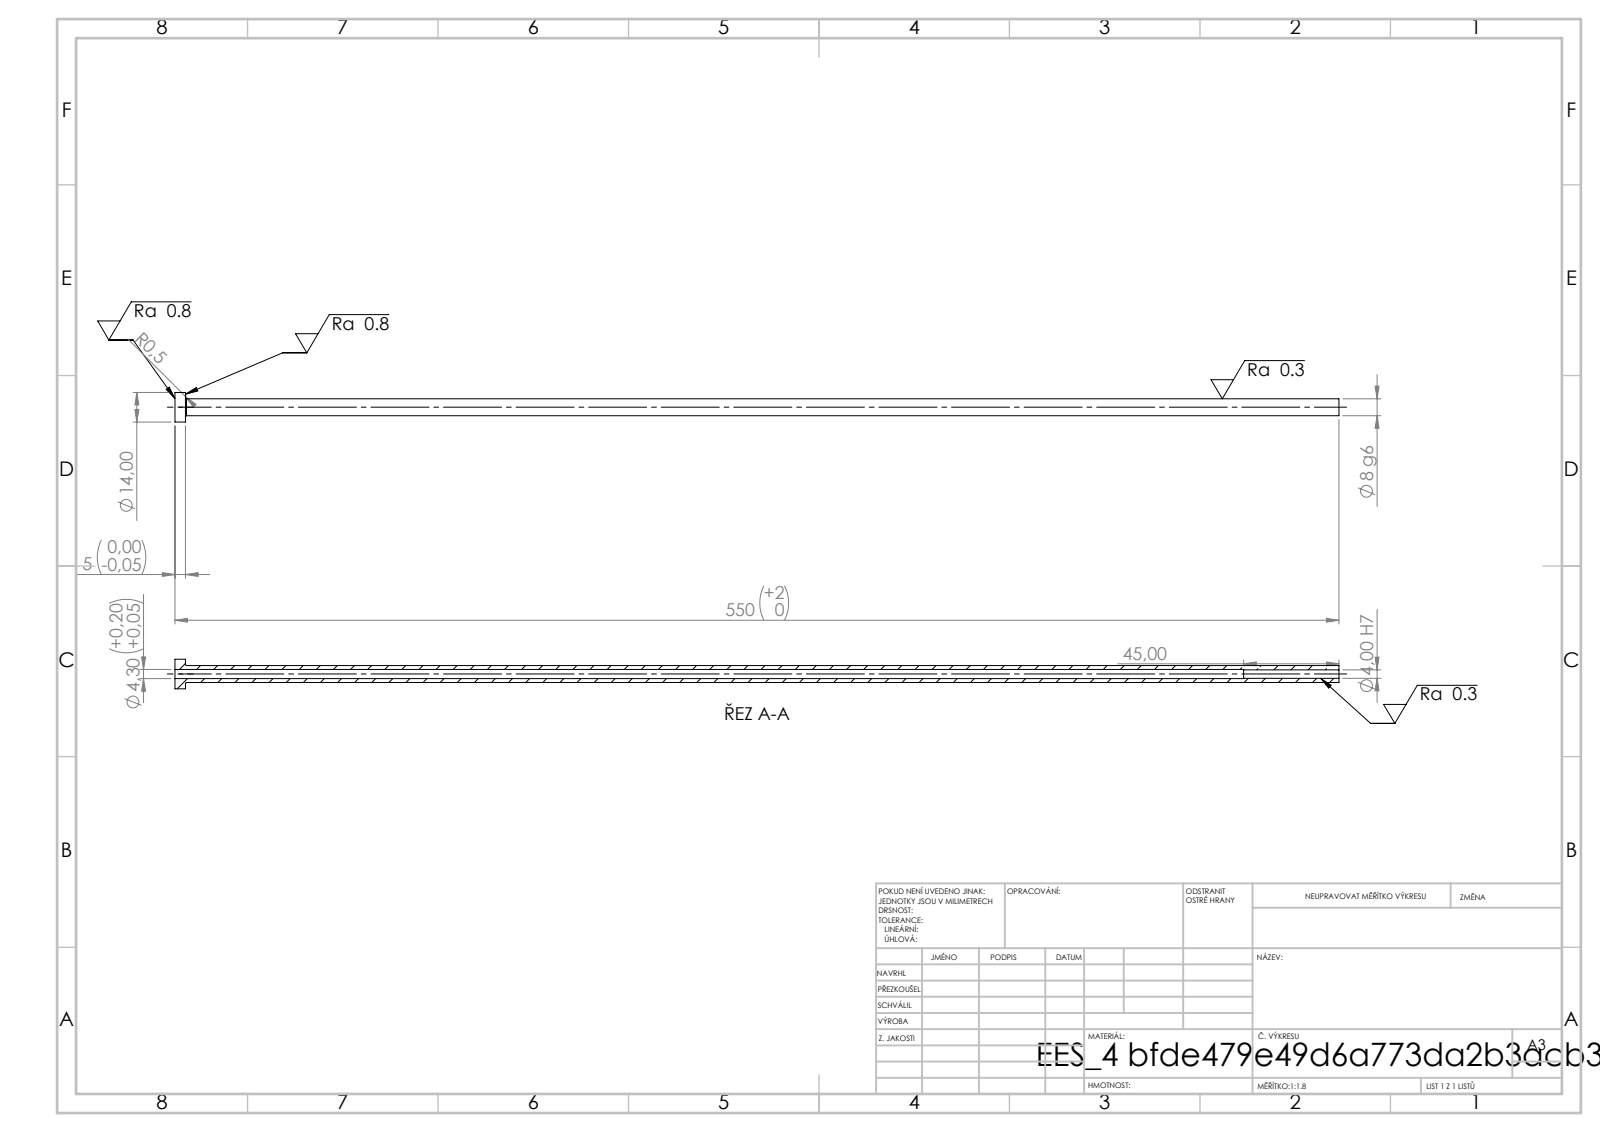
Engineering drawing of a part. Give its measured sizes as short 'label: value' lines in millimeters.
written by: SolidWorks 2019 (CONFIG_CONTROL_DESIGN)
unit: mm
bodies: 1 solid, 14 faces (4 planar, 8 cylindrical, 2 other)
size: 550 × 14 × 14
volume: 20 267 mm³; area: 21 582 mm²
holes: 1× ⌀4, 1× ⌀4.3
bosses: 1× ⌀14, 1× ⌀8
face distances: 5, 550, 545, 505, 500, 45
